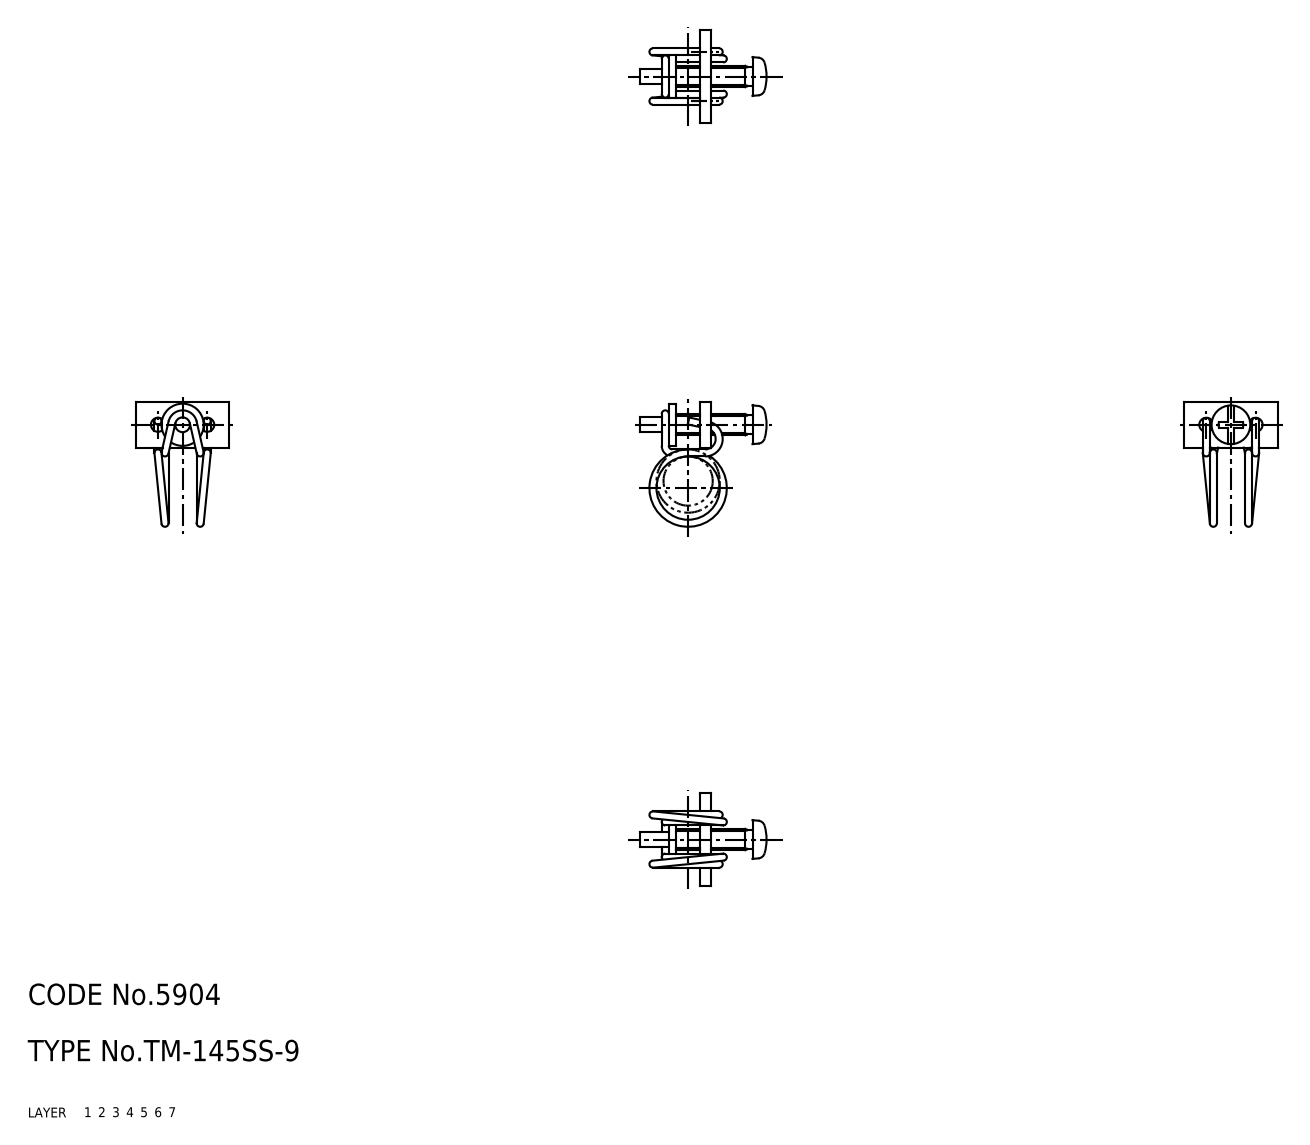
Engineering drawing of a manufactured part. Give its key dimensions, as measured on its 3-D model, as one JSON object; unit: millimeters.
{"part_name": "67115543; 67115556; 67115569", "step_written_by": "CADfix (AUTOMOTIVE_DESIGN)", "units": "millimeters", "bodies": {"solids": 3, "faces": 75, "planar": 0, "cylindrical": 0, "other": 75}, "overall_size": [17.98, 17.75, 13.3], "volume_mm3": 349, "surface_area_mm2": 844}
